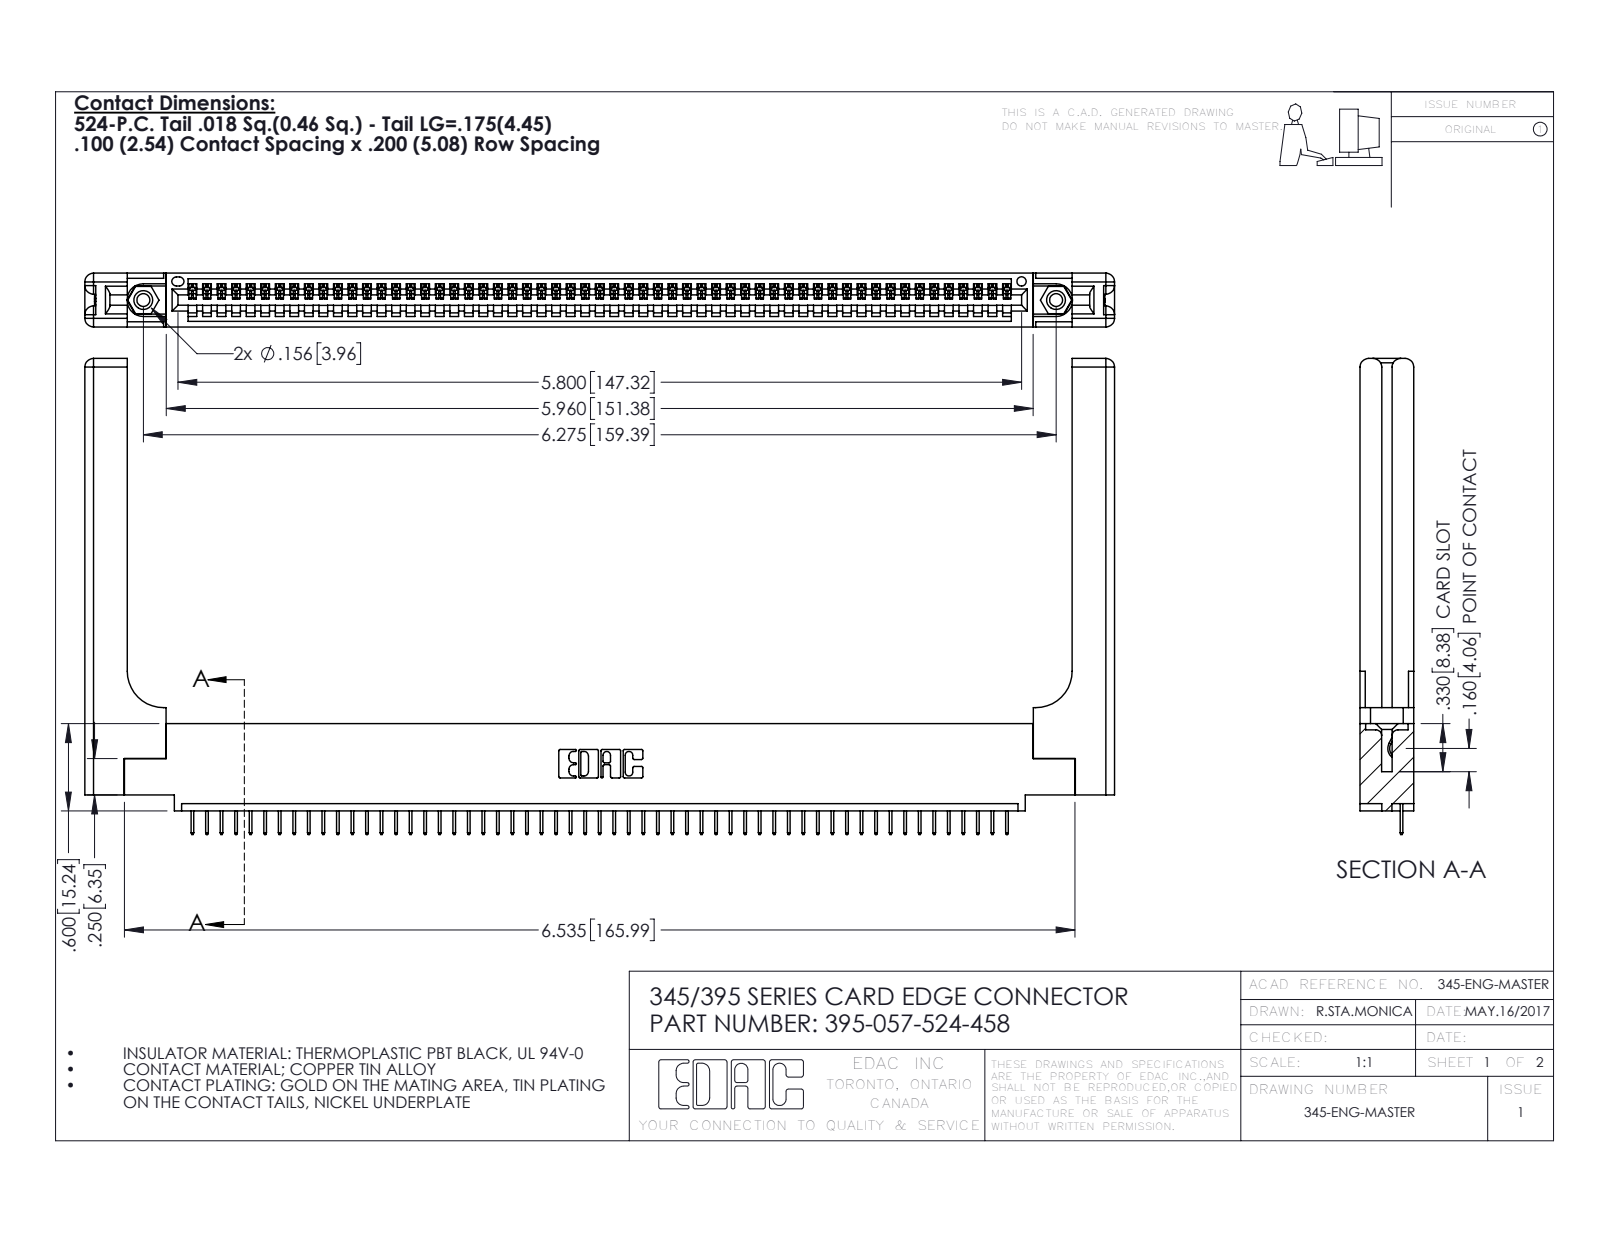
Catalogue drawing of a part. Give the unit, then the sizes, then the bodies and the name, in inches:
Units: inches
Overall size (bounding box): 7.079 × 3.272 × 0.37
Round holes (diameter × count): ⌀0.089 ×2, ⌀0.125 ×2, ⌀0.156 ×2, ⌀0.064 ×1
Round bosses / shafts (diameter × count): ⌀0.155 ×2
Partial cylindrical surfaces — rounded edges, fillets, slot ends (radius × count): R0.006 ×114, R0.01 ×22, R0.06 ×16, R0.007 ×6, R0.031 ×6, R0.026 ×3, R0.03 ×2, R0.031 ×2
Main face-to-face distances: 0.37, 0.072, 0.298, 0.098, 0.272, 0.025, 0.2, 0.225, 0.148, 0.15
Hole centre spacings: 0.27, 6.039, 6.275
Volume: 1.55 in³ · Surface area: 42.37 in²
Bodies: 62 solids, 3920 faces (2854 planar, 1006 cylindrical, 60 other)
Part name (STEP PRODUCT): 395-057-524-458; 345-220-058_345-220-058; 345-250-001_345-250-001-102; 345-292-001_345-293-124 (+1 more)
STEP written by: SolidWorks 2016 (CONFIG_CONTROL_DESIGN)
